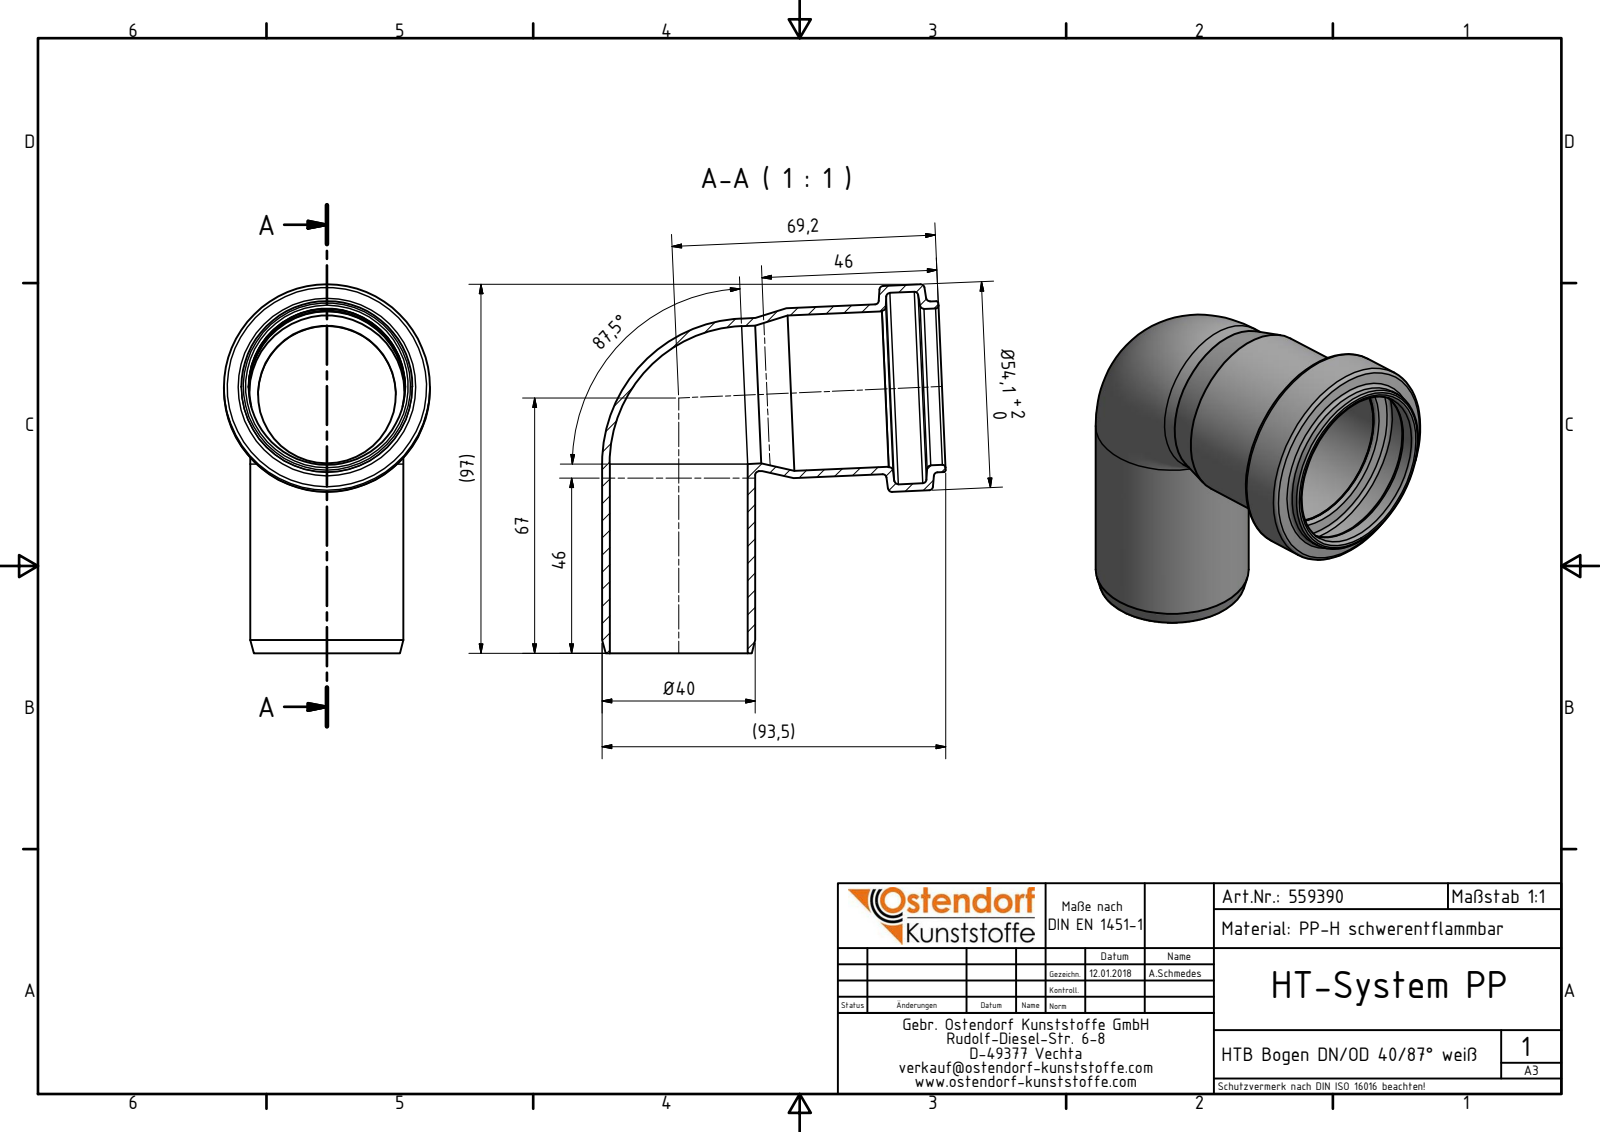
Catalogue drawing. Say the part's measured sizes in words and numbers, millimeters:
The part is named "559390 HTB DN_OD 40_87° weiß". Its 3-D file was written by "Autodesk Inventor 2016 (AUTOMOTIVE_DESIGN)". It is 1 solid with 34 faces: 3 planar, 11 cylindrical and 20 other. Overall it measures 96.85 by 90.19 by 54.1 millimeters. Its volume is 32 860 cubic millimeters and its surface area 35 384 square millimeters. Round holes: 2 of diameter 36.2, 2 of diameter 41.1, 1 of diameter 40.8, 1 of diameter 50.3. Round bosses or shafts: 2 of diameter 40.2, 1 of diameter 54.1, 1 of diameter 44.9, 1 of diameter 44.6. The main face-to-face distances are 14.9.
